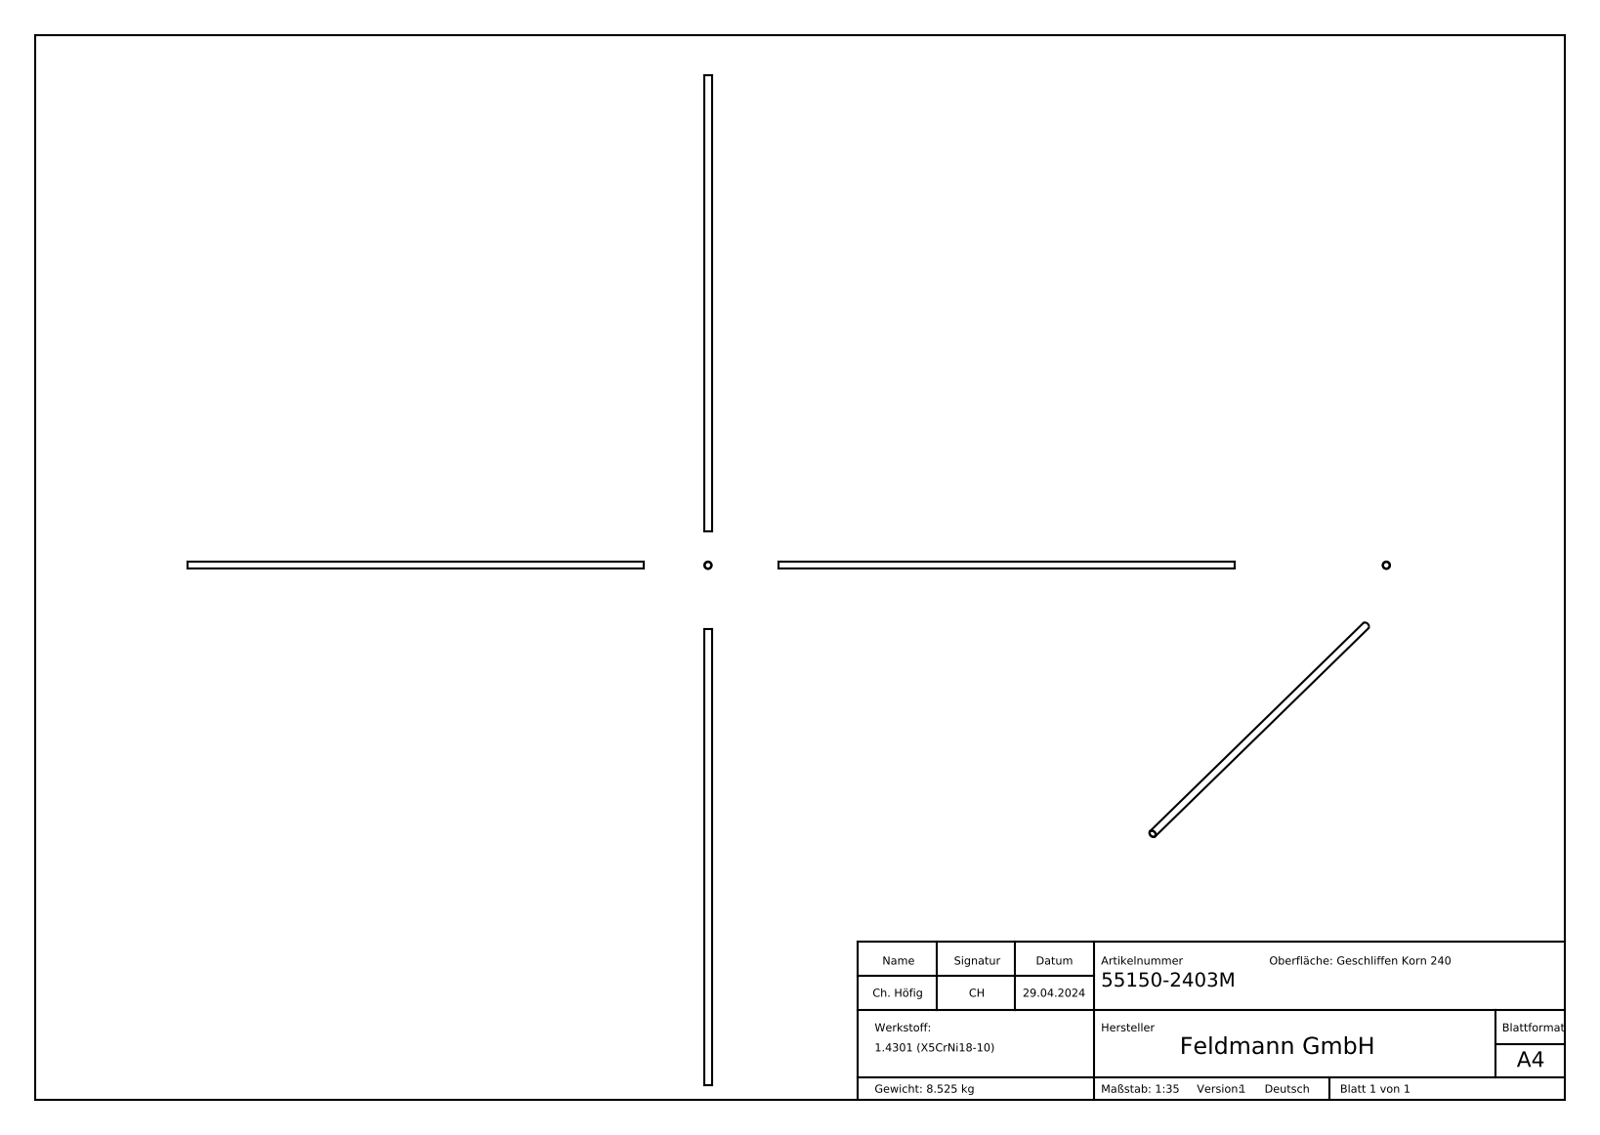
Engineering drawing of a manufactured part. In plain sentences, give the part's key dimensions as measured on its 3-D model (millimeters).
The part is named "55150-2403M". Its 3-D file was written by "SolidWorks 2018 (CONFIG_CONTROL_DESIGN)". It is 1 solid with 299 faces: 141 planar, 28 cylindrical and 130 other. Overall it measures 3000 by 48.3 by 48.3 millimeters. Its volume is 1 079 000 cubic millimeters and its surface area 864 037 square millimeters. Round holes: 1 of diameter 43.3. Round bosses or shafts: 1 of diameter 48.3. Partial cylindrical surfaces (rounded edges, fillets, slot ends): 1 of radius 21.75. The main face-to-face distances are 3000, 1.57, 1.78, 2.41, 0.73, 2.61, 0.79, 0.65, 2.24, 2.45.
